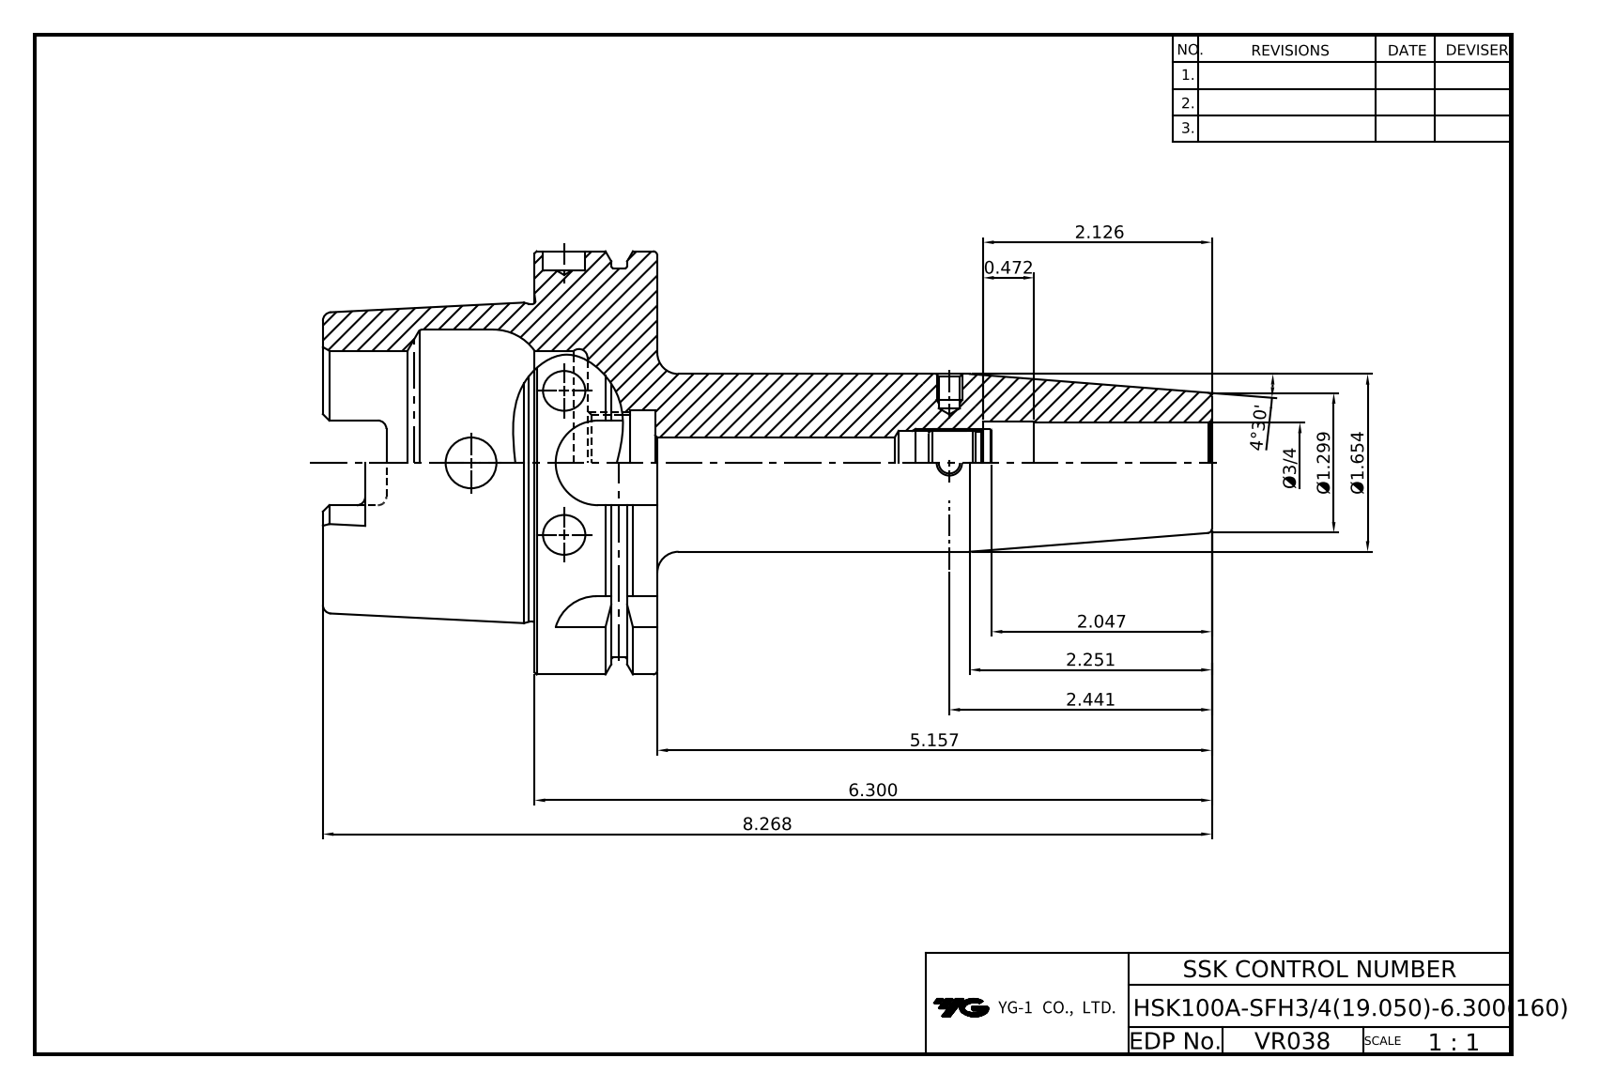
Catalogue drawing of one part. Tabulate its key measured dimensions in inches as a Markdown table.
| quantity | value |
| --- | --- |
| part name | HSK100A-SFH19_05-160 |
| STEP written by | CREO PARAMETRIC BY PTC INC, 2018400 (CONFIG_CONTROL_DESIGN) |
| units | inches |
| bodies | 1 solid, 210 faces (56 planar, 68 cylindrical, 86 other) |
| overall size | 8.268 × 3.937 × 3.937 |
| volume | 23.95 in³ |
| surface area | 114.7 in² |
| round holes (diameter × count) | 0.197 × 2, 0.236 × 2, 0.394 × 1, 0.472 × 1, 0.481 × 1, 0.603 × 1, 0.759 × 1, 0.782 × 1, 0.886 × 1, 0.945 × 1, 0.984 × 1, 2.087 × 1 |
| round bosses / shafts (diameter × count) | 3.937 × 1, 3.622 × 1, 2.959 × 1, 1.662 × 1 |
| partial cylindrical surfaces (radius × count) | 0.079 × 6, 0.192 × 4, 0.394 × 4 |
| main face-to-face distances | 1.142, 0.492, 0.65, 2.461, 1.969, 3.11, 0.394, 2.854, 0.886, 0.256 |
| hole center spacings | 3.583, 4.449 |
